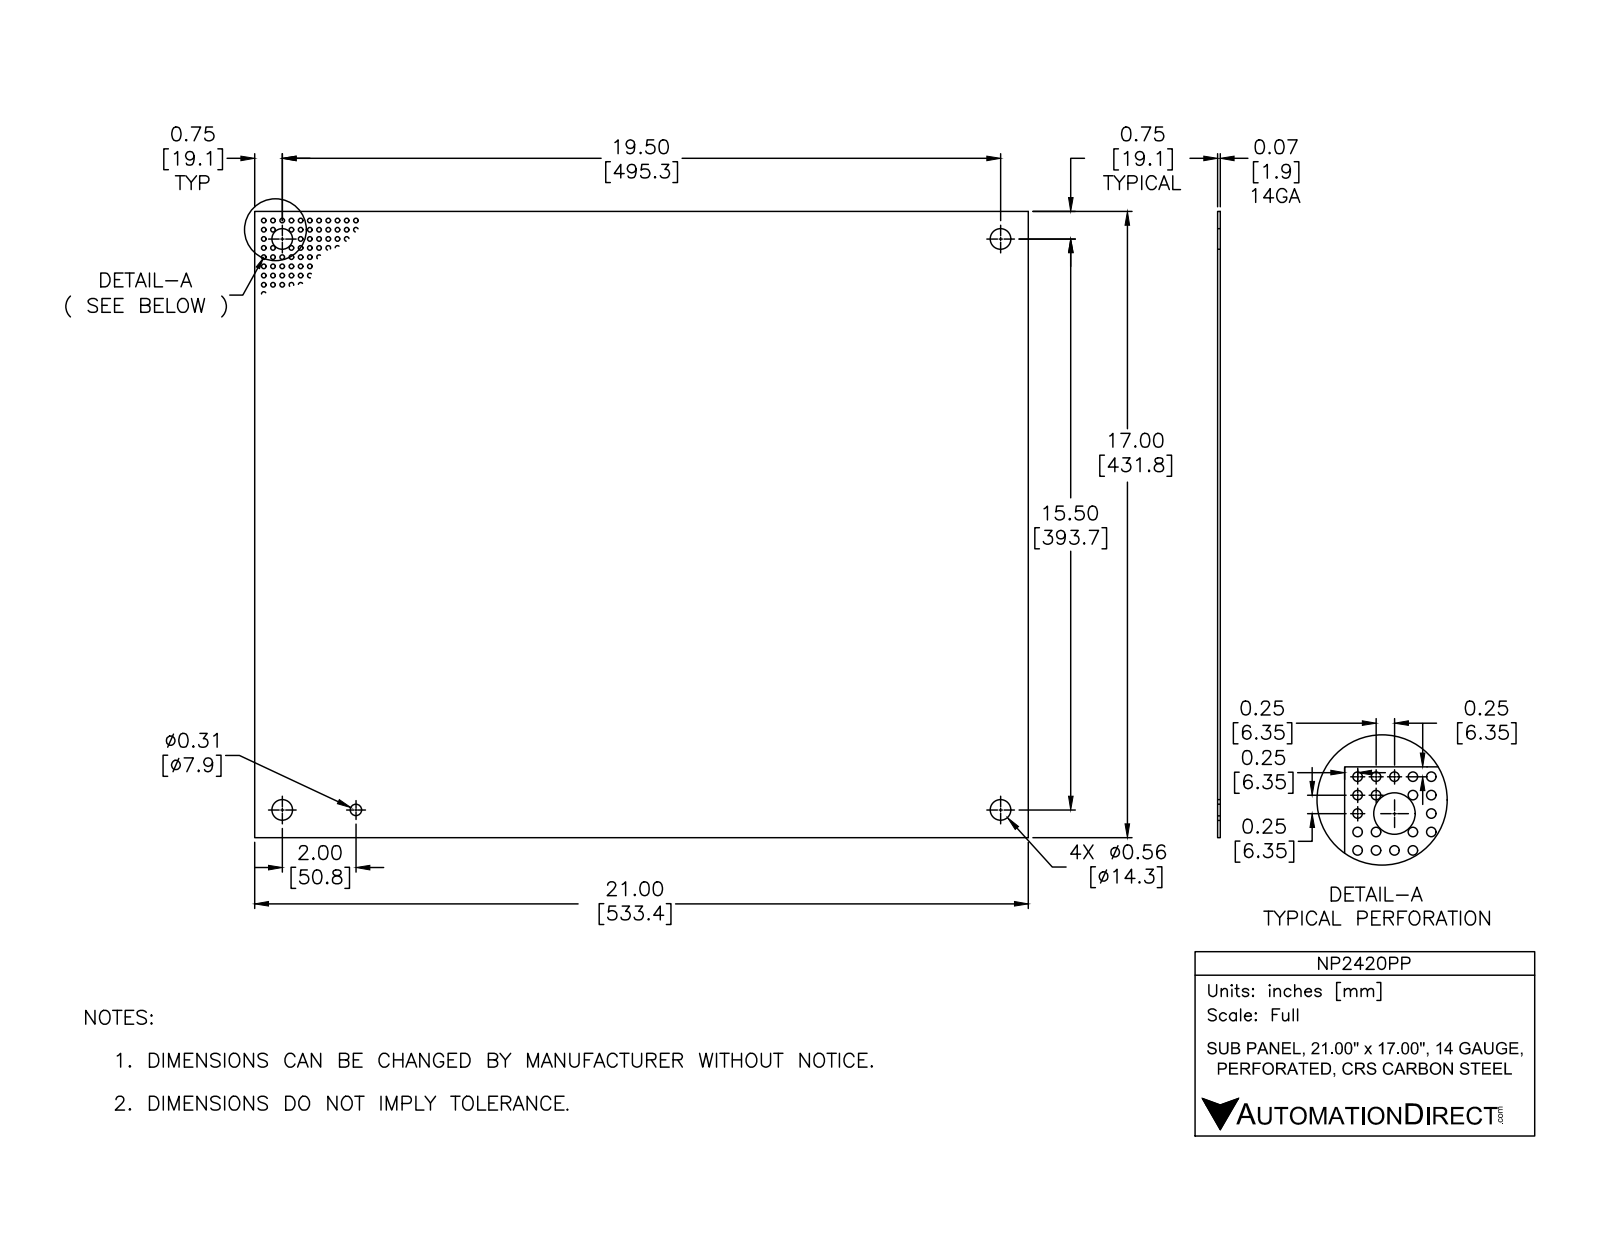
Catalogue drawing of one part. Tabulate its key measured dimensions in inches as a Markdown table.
| quantity | value |
| --- | --- |
| part name | NP2420PP |
| STEP written by | Autodesk Inventor 2012 (AUTOMOTIVE_DESIGN) |
| units | inches |
| bodies | 1 solid, 44 faces (22 planar, 14 cylindrical, 8 other) |
| overall size | 21 × 17 × 0.875 |
| volume | 30.61 in³ |
| surface area | 834.1 in² |
| round holes (diameter × count) | 0.563 × 4, 0.312 × 2 |
| partial cylindrical surfaces (radius × count) | 0.031 × 4, 0.105 × 4 |
| main face-to-face distances | 0.074, 16.926, 20.926, 17, 16.852, 21, 20.852, 0.801, 0.875, 0.126 |
| hole center spacings | 15.25, 19.25, 24.559, 2, 2, 11.25, 13.25, 13.25 |
